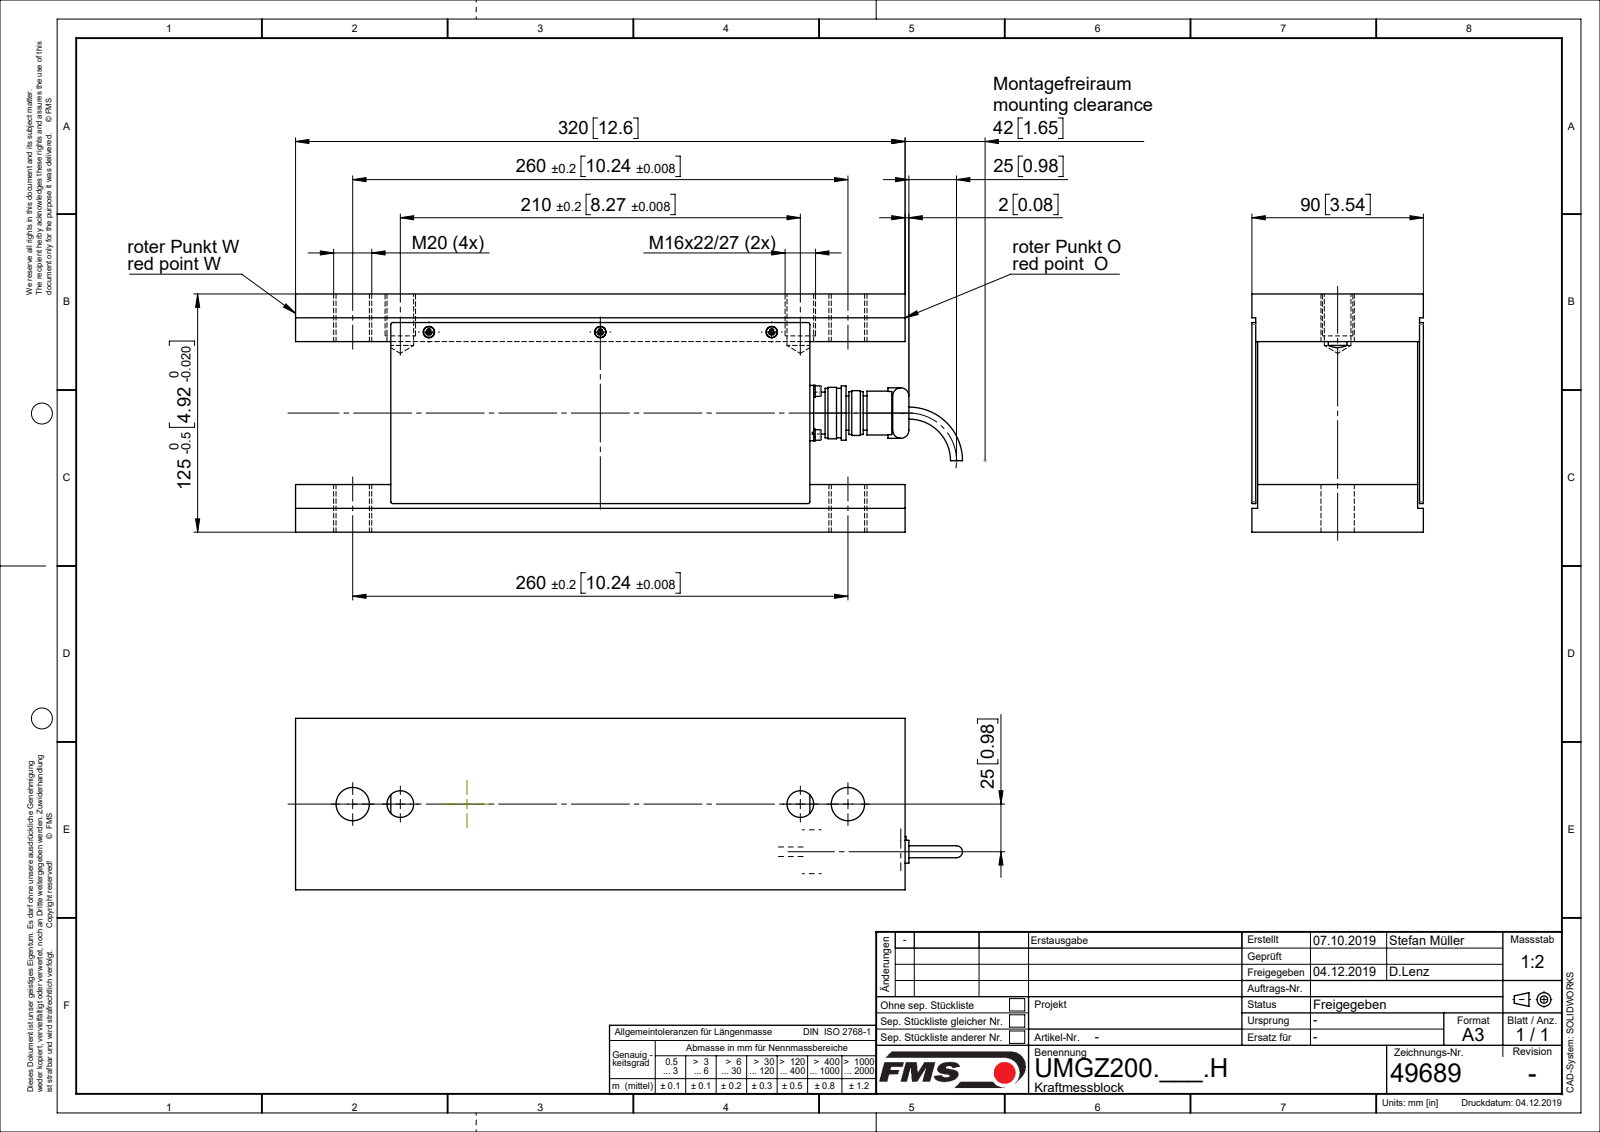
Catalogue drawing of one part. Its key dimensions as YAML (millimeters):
part_name: "U49689; U4812504; U47671; TEIL1 (+5 more)"
step_written_by: "Mechanical Desktop 2007 (CONFIG_CONTROL_DESIGN)"
units: millimeters
bodies: {solids: 18, faces: 379, planar: 133, cylindrical: 162, other: 84}
overall_size: [372.5, 125, 90]
volume: 2856000
surface_area: 271536
round_holes:
  - {diameter: 2.6, count: 7}
  - {diameter: 3.2, count: 4}
  - {diameter: 3.4, count: 3}
  - {diameter: 6, count: 3}
  - {diameter: 14.68, count: 2}
  - {diameter: 17.74, count: 2}
  - {diameter: 20, count: 1}
round_bosses_or_shafts:
  - {diameter: 3, count: 7}
  - {diameter: 6.2, count: 4}
  - {diameter: 5.5, count: 4}
  - {diameter: 2.5, count: 4}
  - {diameter: 28, count: 1}
  - {diameter: 23, count: 1}
  - {diameter: 22, count: 1}
  - {diameter: 21, count: 1}
partial_cylinders:
  - {radius: 4, count: 4}
face_to_face_distances: [2, 88, 85, 3, 1, 87, 90, 125, 86, 84]
hole_center_spacings: [23, 25, 32.53, 90, 235, 35, 60, 175]
